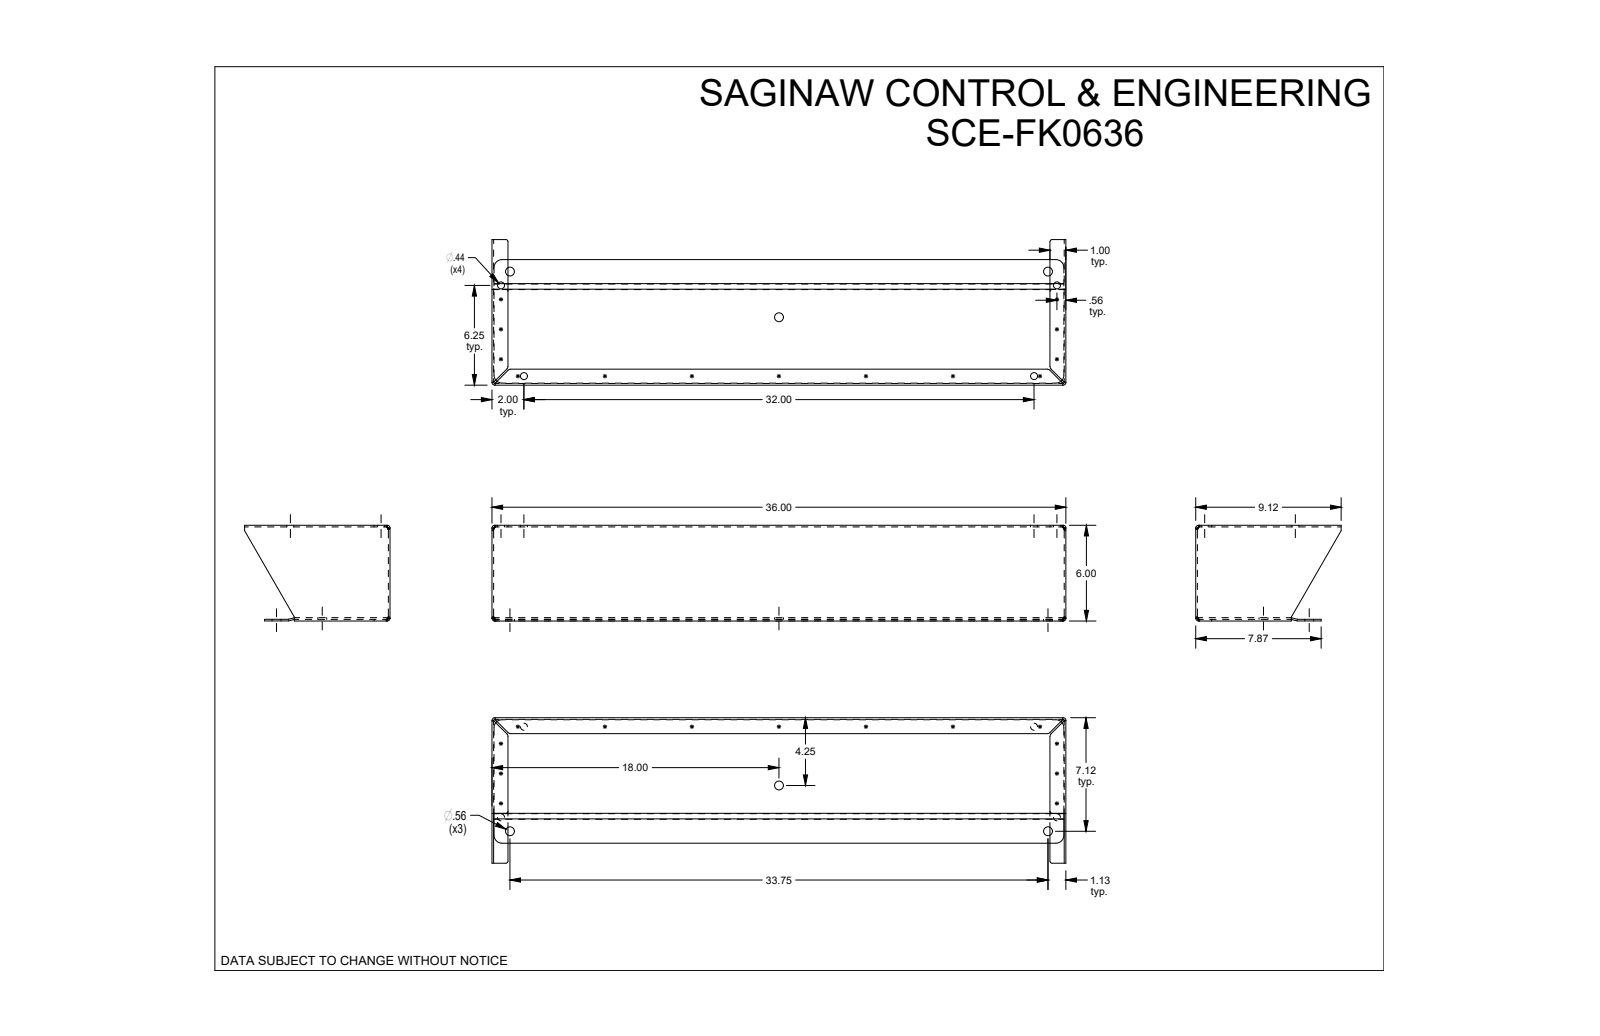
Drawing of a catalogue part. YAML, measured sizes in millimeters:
part_name: "SCE-FK0636"
step_written_by: "SolidWorks 2019 (CONFIG_CONTROL_DESIGN)"
units: millimeters
bodies: {solids: 4, faces: 214, planar: 96, cylindrical: 86, other: 32}
overall_size: [914.4, 609.6, 152.4]
volume: 2260000
surface_area: 1740000
round_holes:
  - {diameter: 11.1, count: 8}
  - {diameter: 14.2, count: 6}
partial_cylinders:
  - {radius: 4.2, count: 16}
  - {radius: 1.6, count: 10}
  - {radius: 3.2, count: 8}
  - {radius: 5.6, count: 8}
  - {radius: 12.7, count: 8}
  - {radius: 1.6, count: 6}
face_to_face_distances: [2.6, 607, 2.6, 604.3, 609.6, 149.7, 147.1, 911.8, 149.8, 5.2]
hole_center_spacings: [26.3, 149, 168, 270.4, 415.1, 417.1, 438.1, 445.8]
